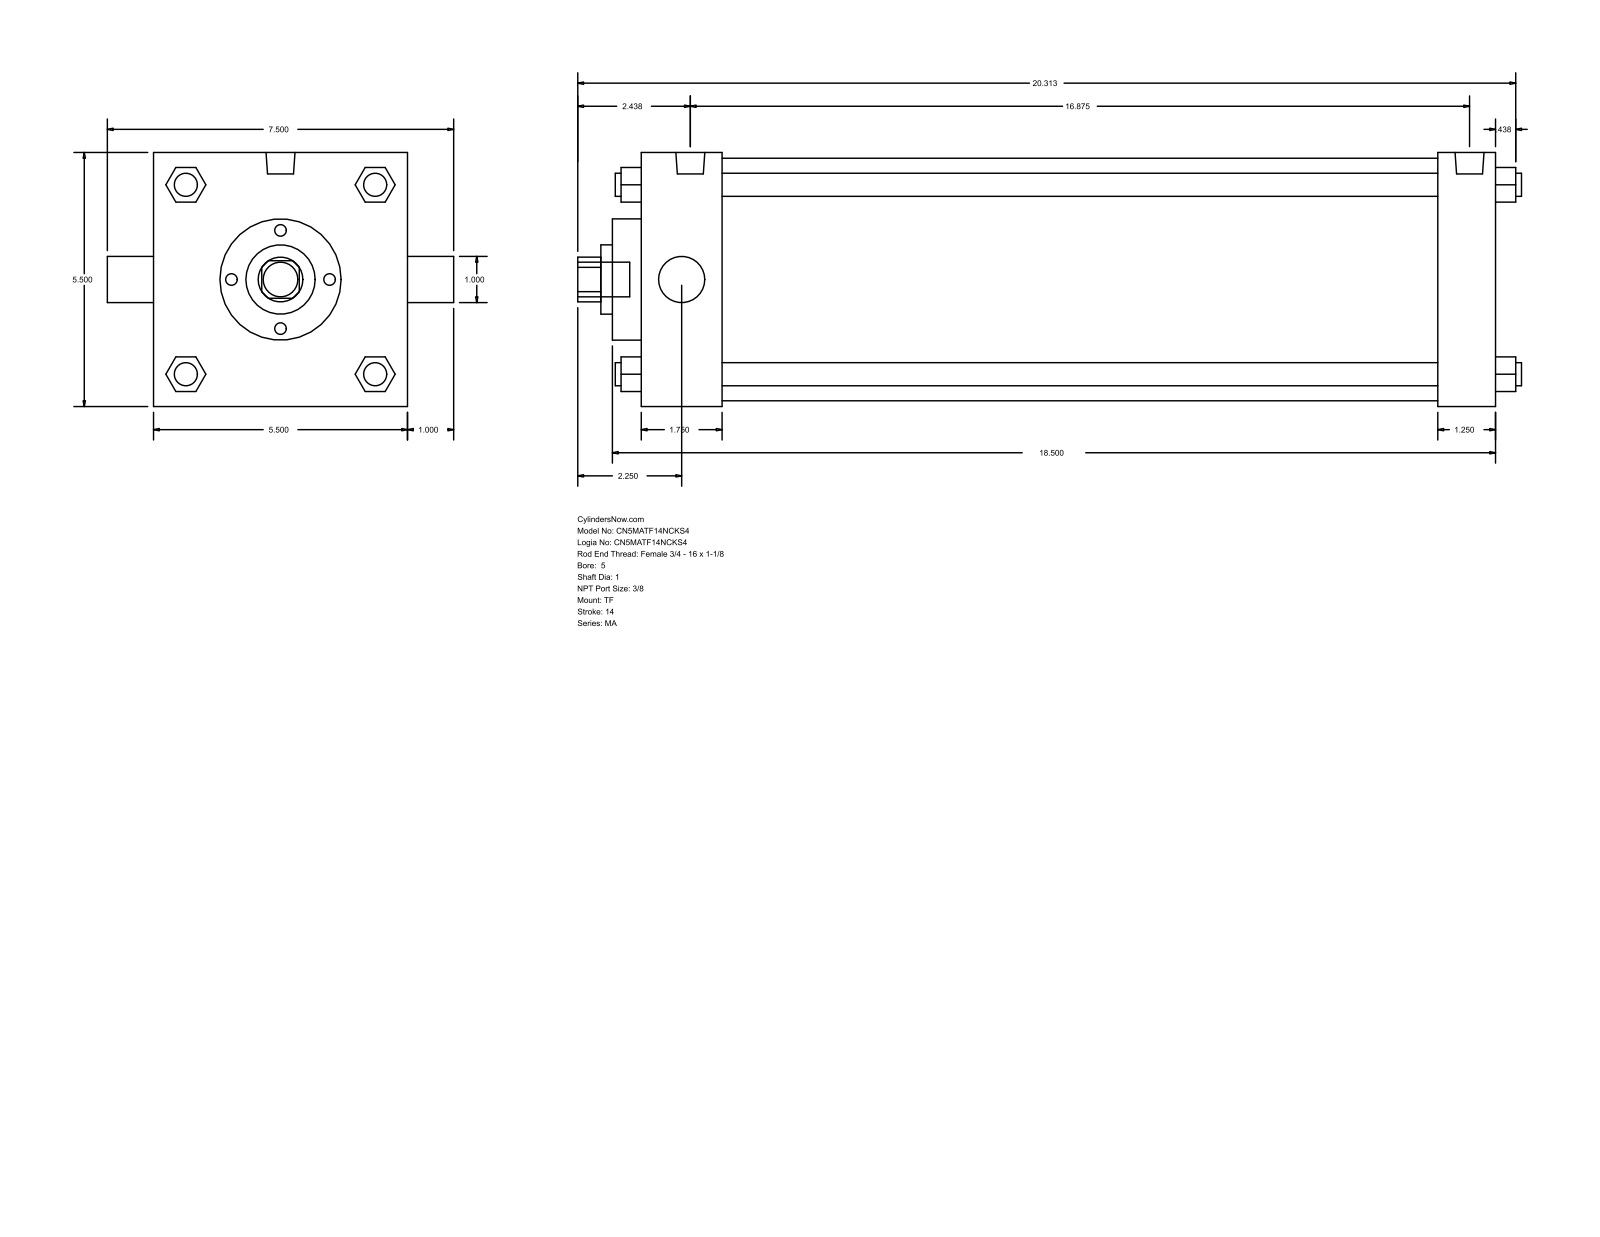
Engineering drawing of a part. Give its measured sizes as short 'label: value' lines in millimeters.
name: MA_TF__0500_1
written by: GSSL Pune (CONFIG_CONTROL_DESIGN)
unit: mm
bodies: 0 solids, 122 faces (93 planar, 29 cylindrical, 0 other)
size: 519.11 × 190.5 × 139.7
holes: 2× ⌀25.4, 1× ⌀38.1, 1× ⌀66.67, 1× ⌀133.35
bosses: 4× ⌀12.7, 3× ⌀11.11, 2× ⌀15.93, 1× ⌀19.05
rounds: 1× R12.29
face distances: 139.7, 469.9, 438.15, 31.75, 44.46, 393.69, 425.44, 15.87, 60.33, 454.02
